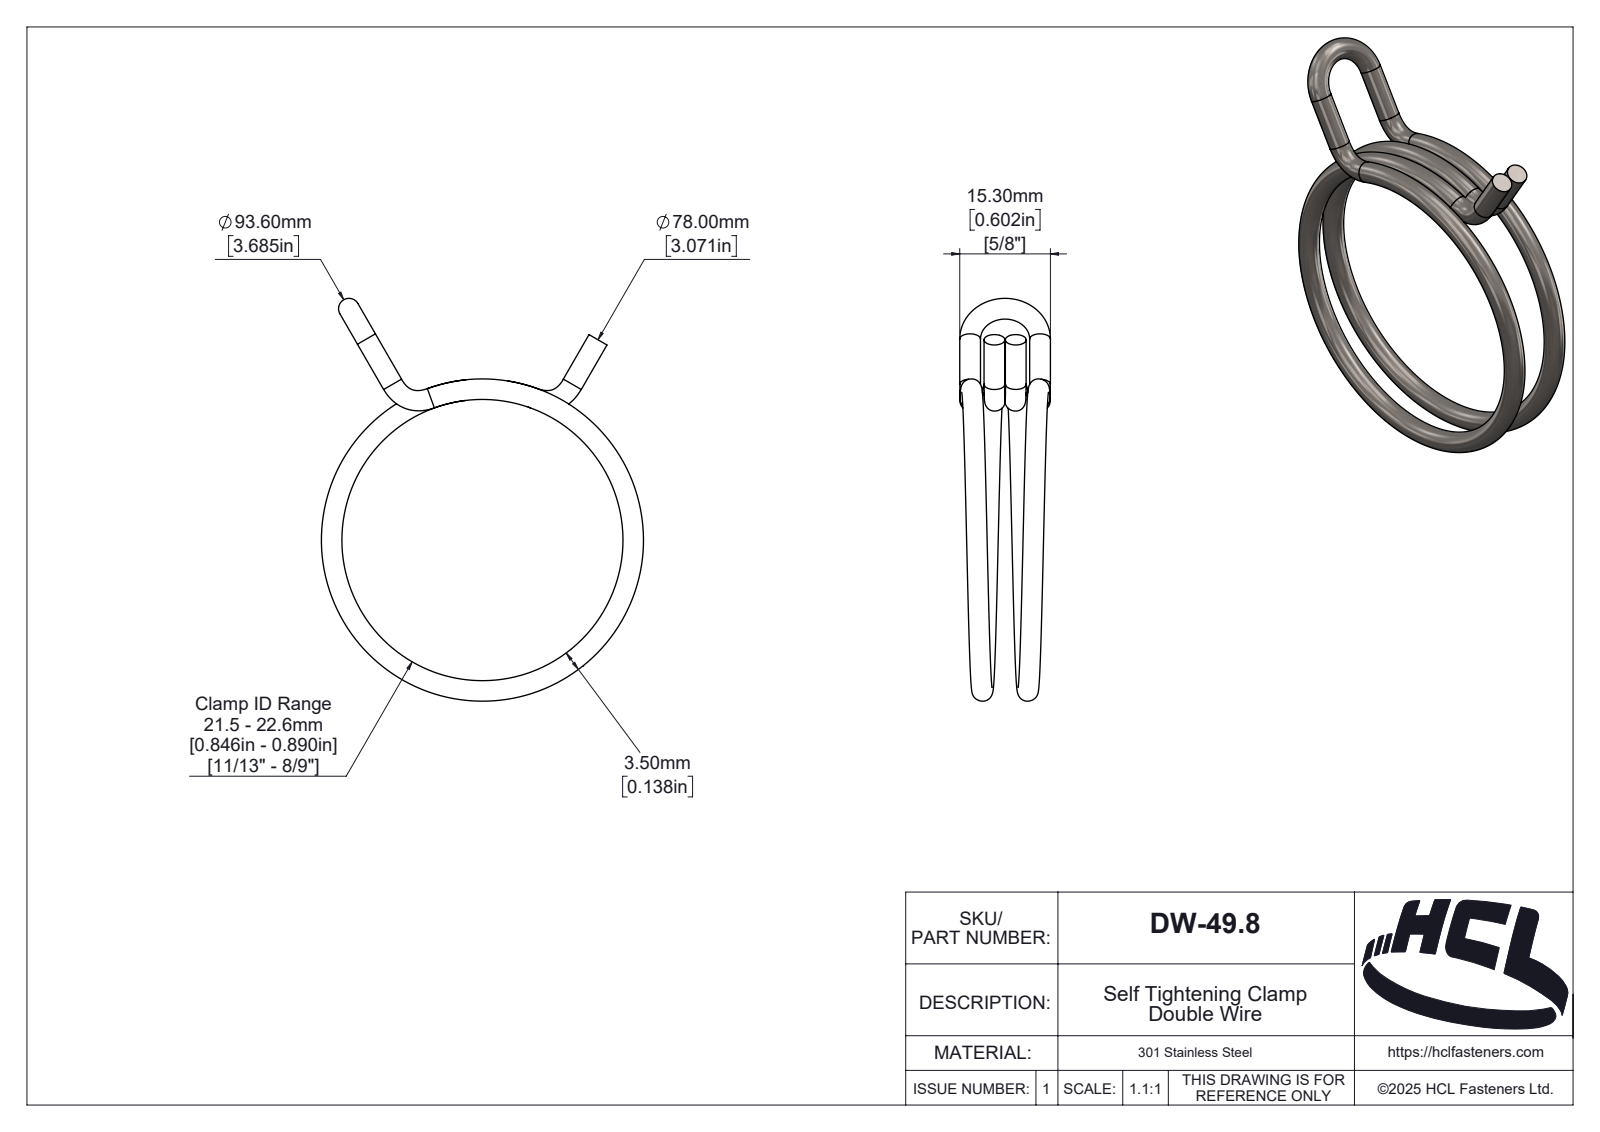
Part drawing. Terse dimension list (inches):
name: DW-49.8
written by: SolidWorks 2025 (AUTOMOTIVE_DESIGN)
unit: in
bodies: 1 solid, 132 faces (14 planar, 53 cylindrical, 65 other)
size: 2.675 × 2.14 × 0.602
volume: 0.254 in³; area: 7.463 in²
bosses: 4× ⌀0.138
rounds: 1× R0.006, 1× R0.008, 1× R0.008, 1× R0.01, 1× R0.014, 1× R0.019, 1× R0.024, 1× R0.027
